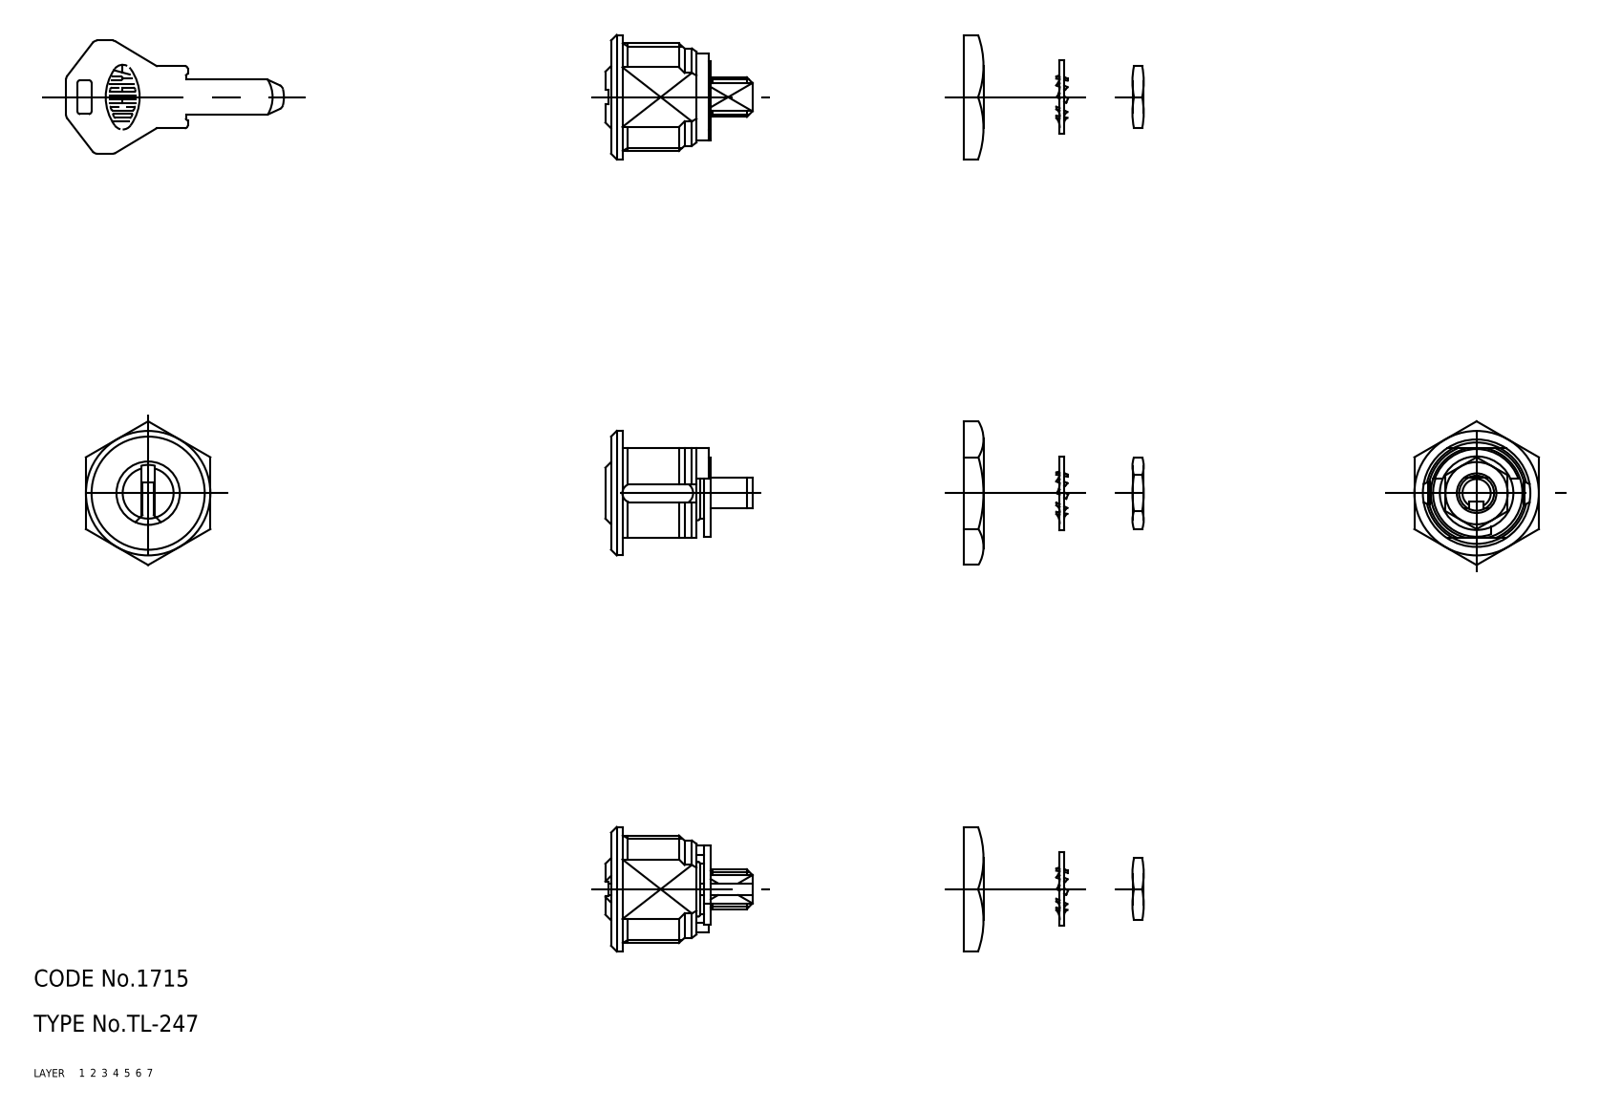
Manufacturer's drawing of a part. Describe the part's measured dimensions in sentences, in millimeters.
The part is named "washer; nut_B; nut_A; lock (+3 more)". Its 3-D file was written by "CADfix (AUTOMOTIVE_DESIGN)". It is 6 solids with 168 faces: 0 planar, 0 cylindrical and 168 other. Overall it measures 94.03 by 25.4 by 22 millimeters. Its volume is 5 717 cubic millimeters and its surface area 4 834 square millimeters.
